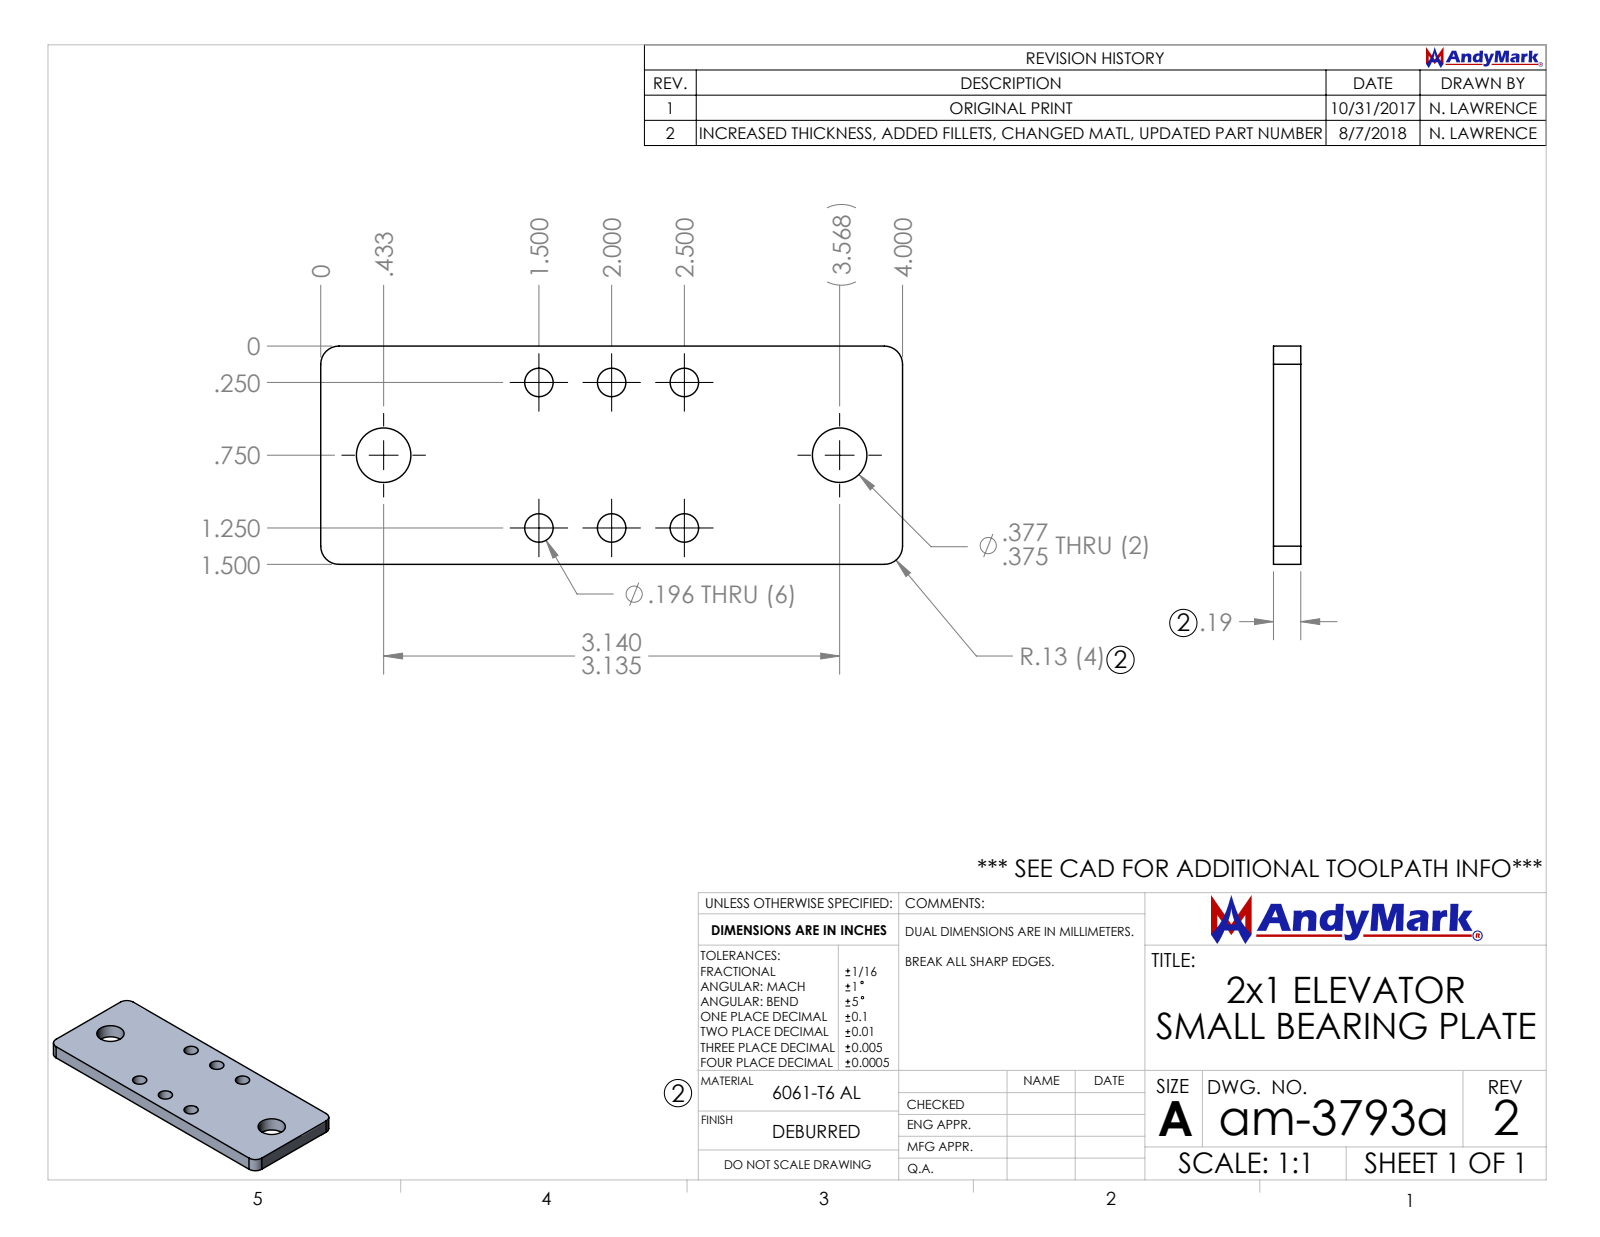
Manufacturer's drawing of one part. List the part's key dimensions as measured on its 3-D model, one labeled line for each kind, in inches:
Part name (STEP PRODUCT): am-3793a 2x1 Elevator Small Bearing Plate R2
STEP written by: SolidWorks 2018 (AUTOMOTIVE_DESIGN)
Units: inches
Bodies: 1 solid, 18 faces (6 planar, 12 cylindrical, 0 other)
Overall size (bounding box): 4 × 1.5 × 0.188
Volume: 1.047 in³ · Surface area: 14.33 in²
Round holes (diameter × count): ⌀0.196 ×6, ⌀0.375 ×2
Partial cylindrical surfaces — rounded edges, fillets, slot ends (radius × count): R0.125 ×4
Main face-to-face distances: 0.187, 1.5, 4
Hole centre spacings: 1, 0.5, 1.118, 1.179, 1.645, 2.127, 1.414, 3.135
